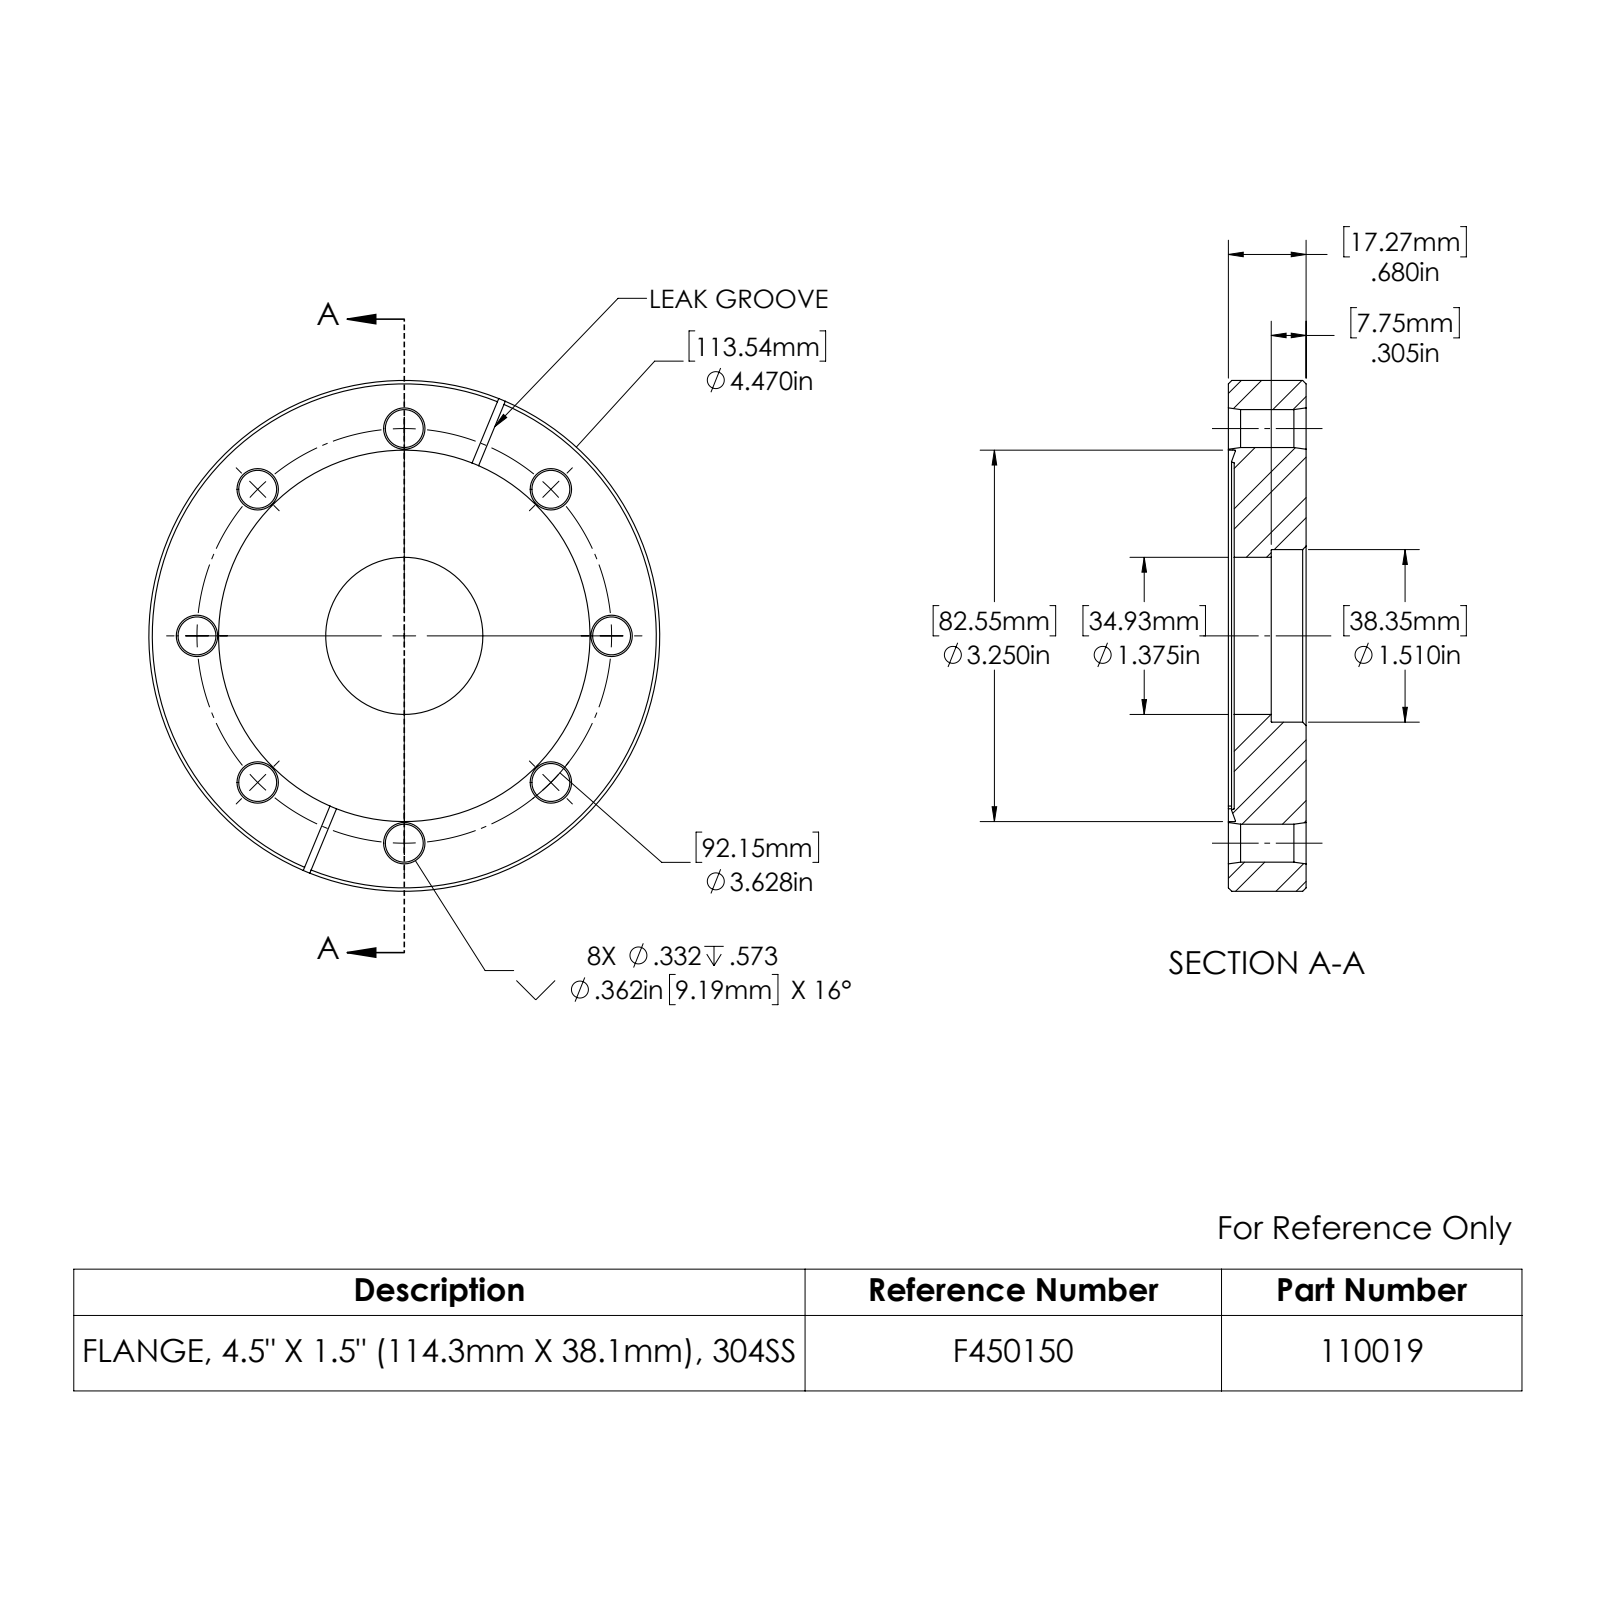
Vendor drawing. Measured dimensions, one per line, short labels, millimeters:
name: 110019_A
written by: SolidWorks 2022 (CONFIG_CONTROL_DESIGN)
unit: mm
bodies: 1 solid, 86 faces (11 planar, 24 cylindrical, 51 other)
size: 113.5 × 113.5 × 17.3
volume: 143 000 mm³; area: 29 220 mm²
holes: 8× ⌀8.4, 1× ⌀34.9, 1× ⌀38.4, 1× ⌀82.6
bosses: 1× ⌀113.5
face distances: 17.3, 1.3, 16, 9.5, 8.2, 7.7, 1.3, 8.2, 16, 1.5
hole spacings: 35.3, 46.1, 85.1, 65.2, 65.2, 92.2, 92.2
